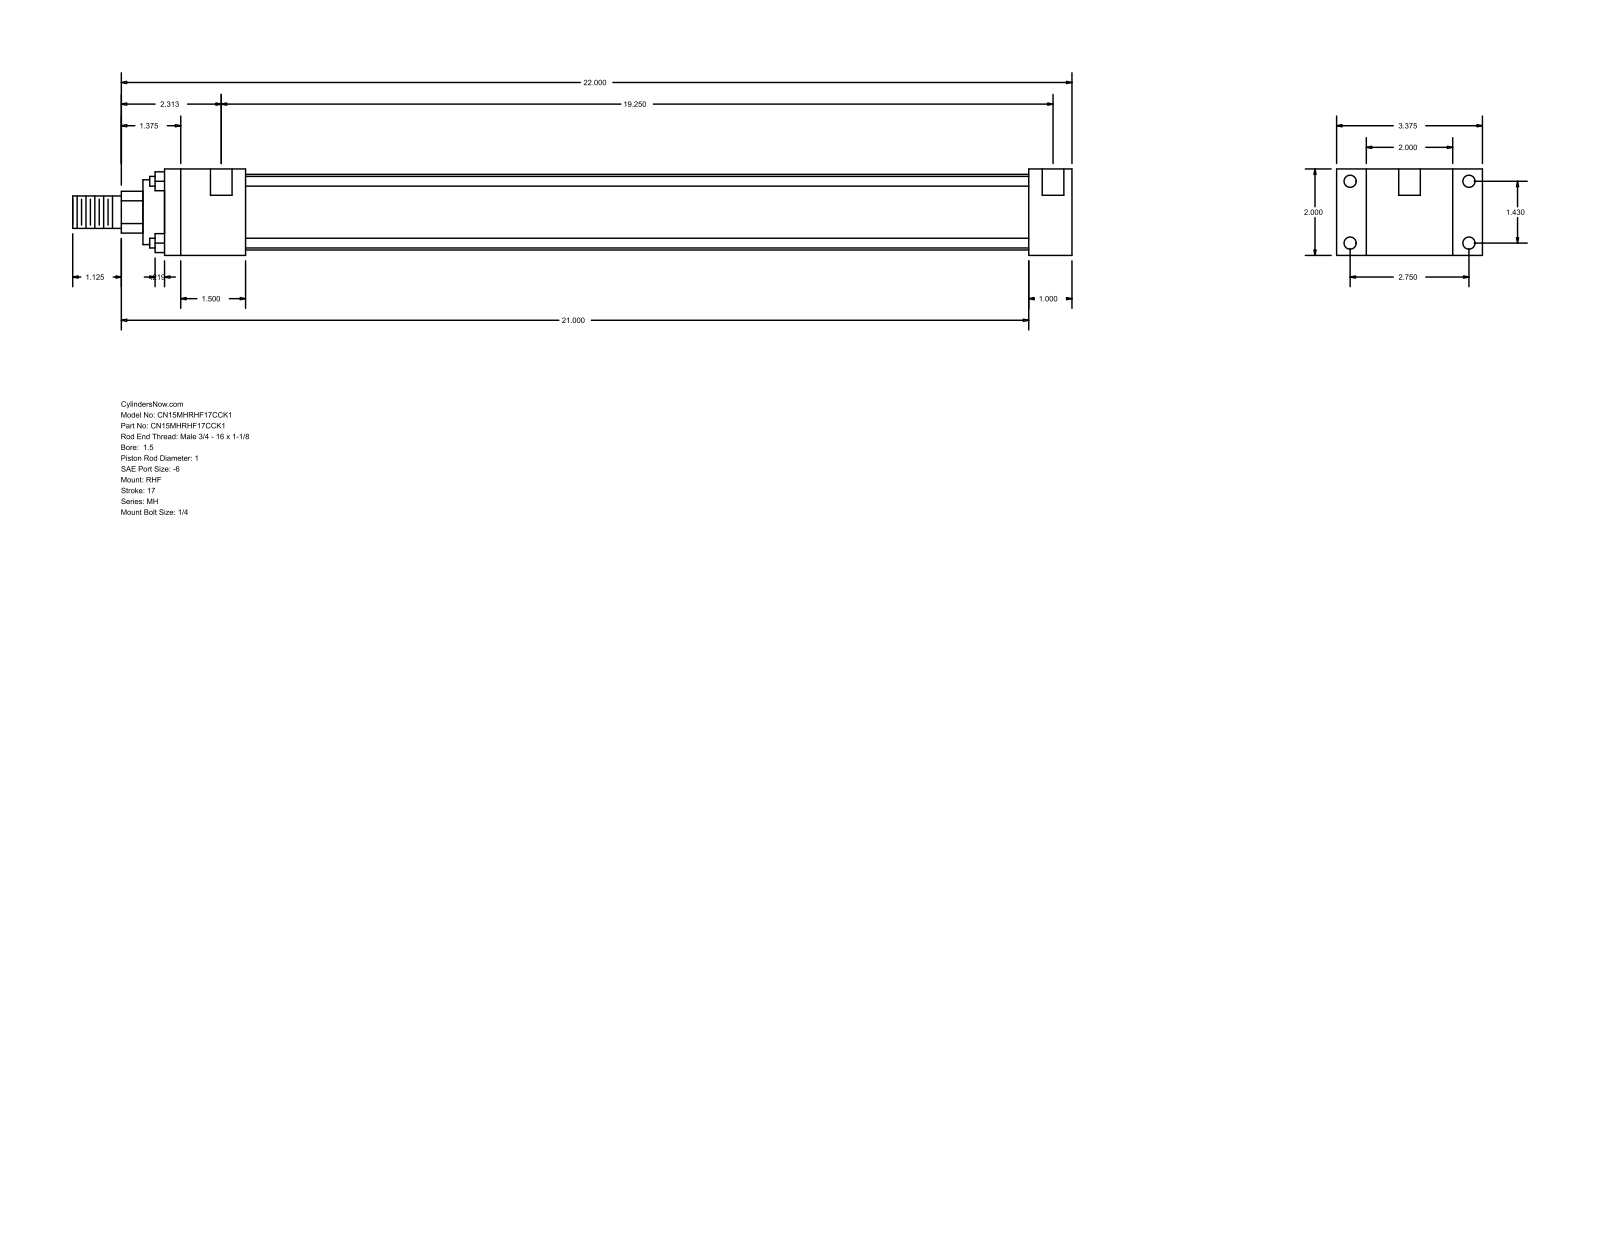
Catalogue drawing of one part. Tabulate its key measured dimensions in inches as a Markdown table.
| quantity | value |
| --- | --- |
| part name | MH_RHF__0150_1 |
| STEP written by | GSSL Pune (CONFIG_CONTROL_DESIGN) |
| units | inches |
| bodies | 0 solids, 88 faces (60 planar, 28 cylindrical, 0 other) |
| overall size | 23.125 × 3.375 × 2 |
| round holes (diameter × count) | 0.219 × 4, 0.281 × 4, 0.5 × 2 |
| round bosses / shafts (diameter × count) | 0.225 × 4, 1.75 × 1, 1.5 × 1, 1 × 1, 0.75 × 1 |
| partial cylindrical surfaces (radius × count) | 0.484 × 1 |
| main face-to-face distances | 2, 1, 0.687, 2.687, 3.375, 21, 20, 1.875, 18.125, 19.125 |
| hole center spacings | 1.43, 2.75, 3.099, 19.375, 0.125, 19.25 |
